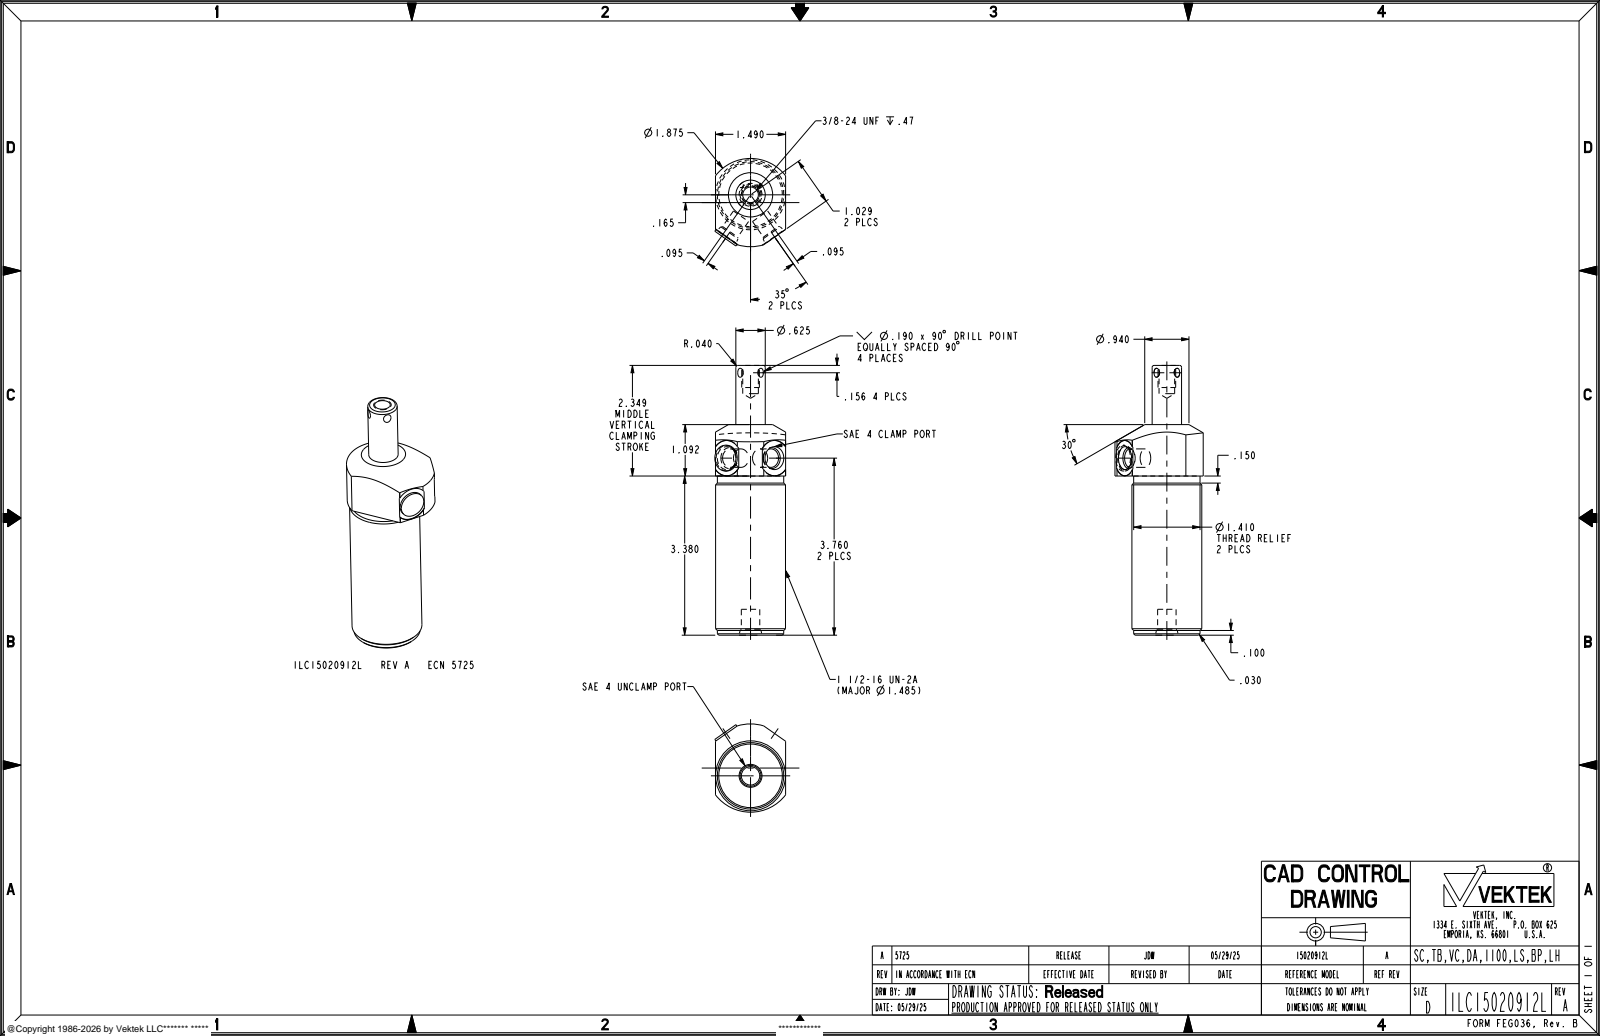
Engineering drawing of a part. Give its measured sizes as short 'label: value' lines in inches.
name: ILC15020912L
written by: CREO PARAMETRIC BY PTC INC, 2021164 (AUTOMOTIVE_DESIGN)
unit: in
bodies: 1 solid, 80 faces (18 planar, 30 cylindrical, 32 other)
size: 5.729 × 1.875 × 1.504
volume: 8.325 in³; area: 31.82 in²
holes: 3× ⌀0.392, 1× ⌀0.332
bosses: 1× ⌀1.485, 1× ⌀1.41, 1× ⌀0.625, 1× ⌀0.547, 1× ⌀0.375
rounds: 2× R0.375, 1× R0.937
face distances: 1.49, 3.38, 4.472, 1.092, 0.53, 0.05, 5.729, 2.349, 1.257, 0.58
